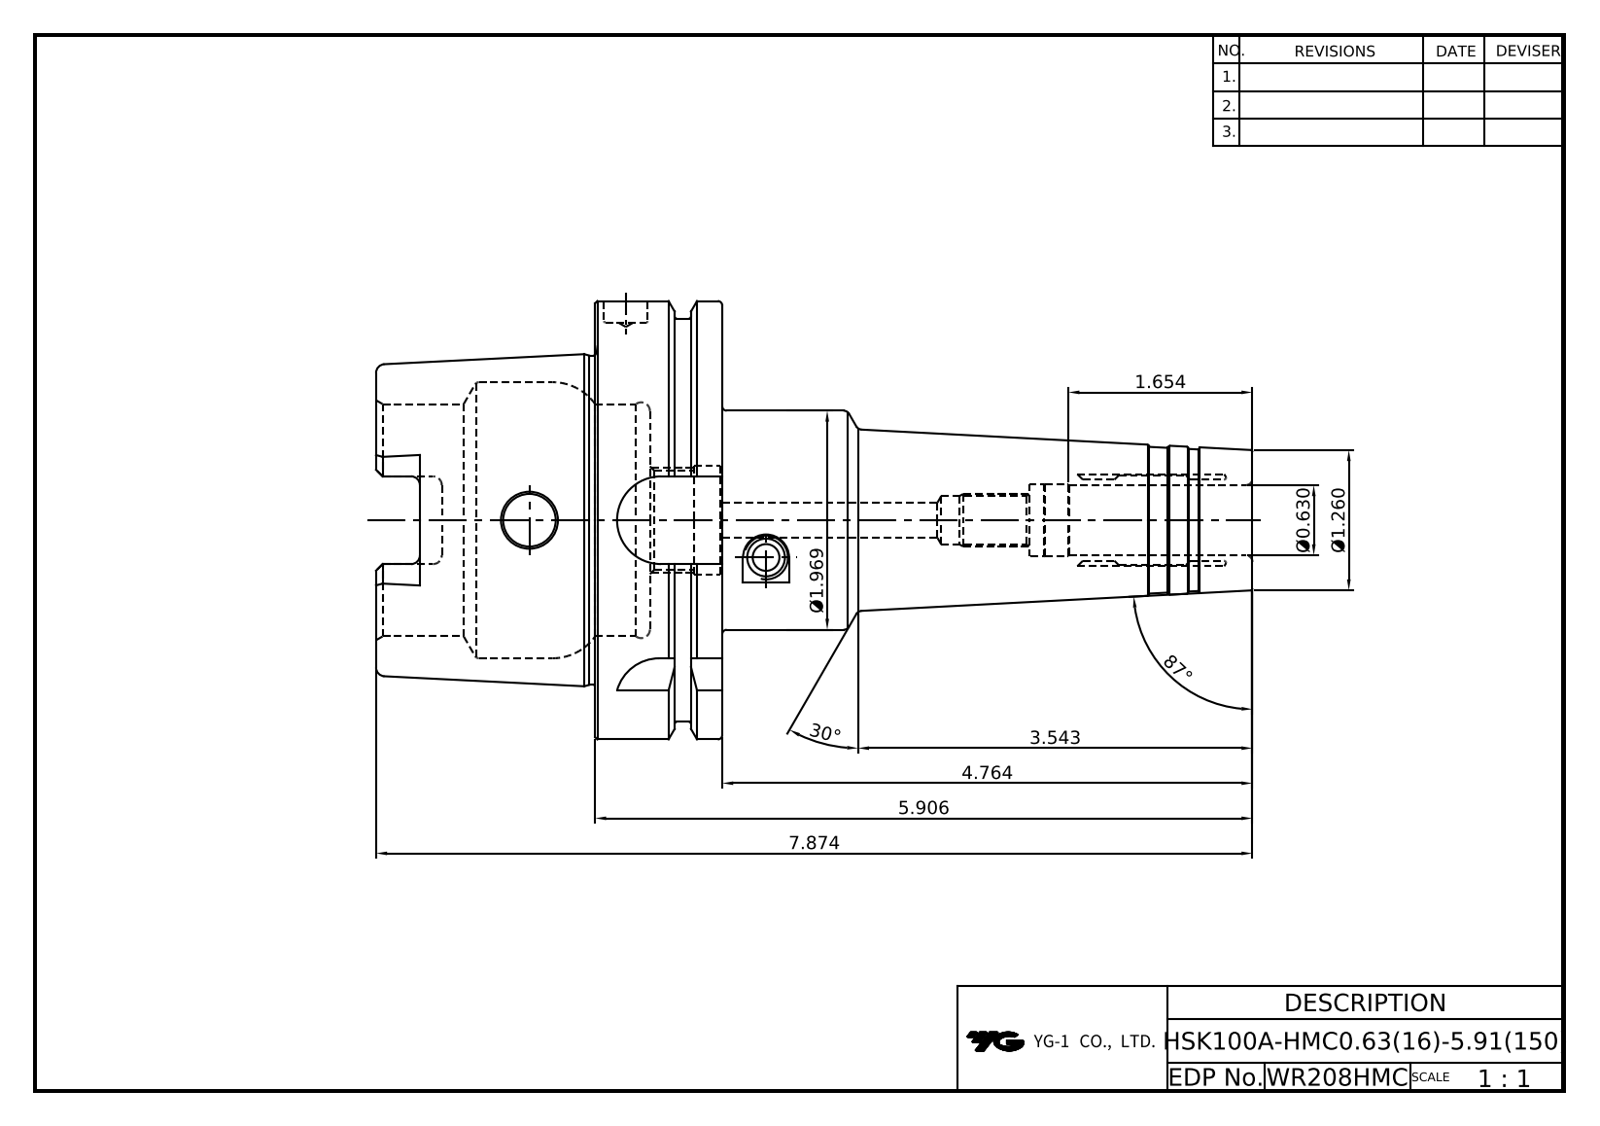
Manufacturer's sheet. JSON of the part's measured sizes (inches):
{"part_name": "WR208HMC-HSK100A-HMC0_63-5_91", "step_written_by": "PRO/ENGINEER BY PARAMETRIC TECHNOLOGY CORPORATION, 2012130 (CONFIG_CONTROL_DESIGN)", "units": "inches", "bodies": {"solids": 1, "faces": 210, "planar": 52, "cylindrical": 54, "other": 104}, "overall_size": [7.874, 3.937, 3.937], "volume_in3": 23.93, "surface_area_in2": 108.4, "round_holes": [[0.315, 1], [0.394, 1], [0.437, 1], [0.472, 1], [0.63, 1], [0.646, 1], [0.654, 1], [0.886, 1], [0.945, 1], [0.984, 1], [2.087, 1], [2.518, 1]], "round_bosses_or_shafts": [[3.937, 1], [3.622, 1], [2.959, 1], [1.968, 1]], "partial_cylinders_radius": [[0.079, 6], [0.192, 4], [0.394, 4]], "face_to_face_distances": [1.142, 0.492, 0.65, 2.461, 3.11, 1.969, 0.394, 2.854, 0.886, 0.256]}
